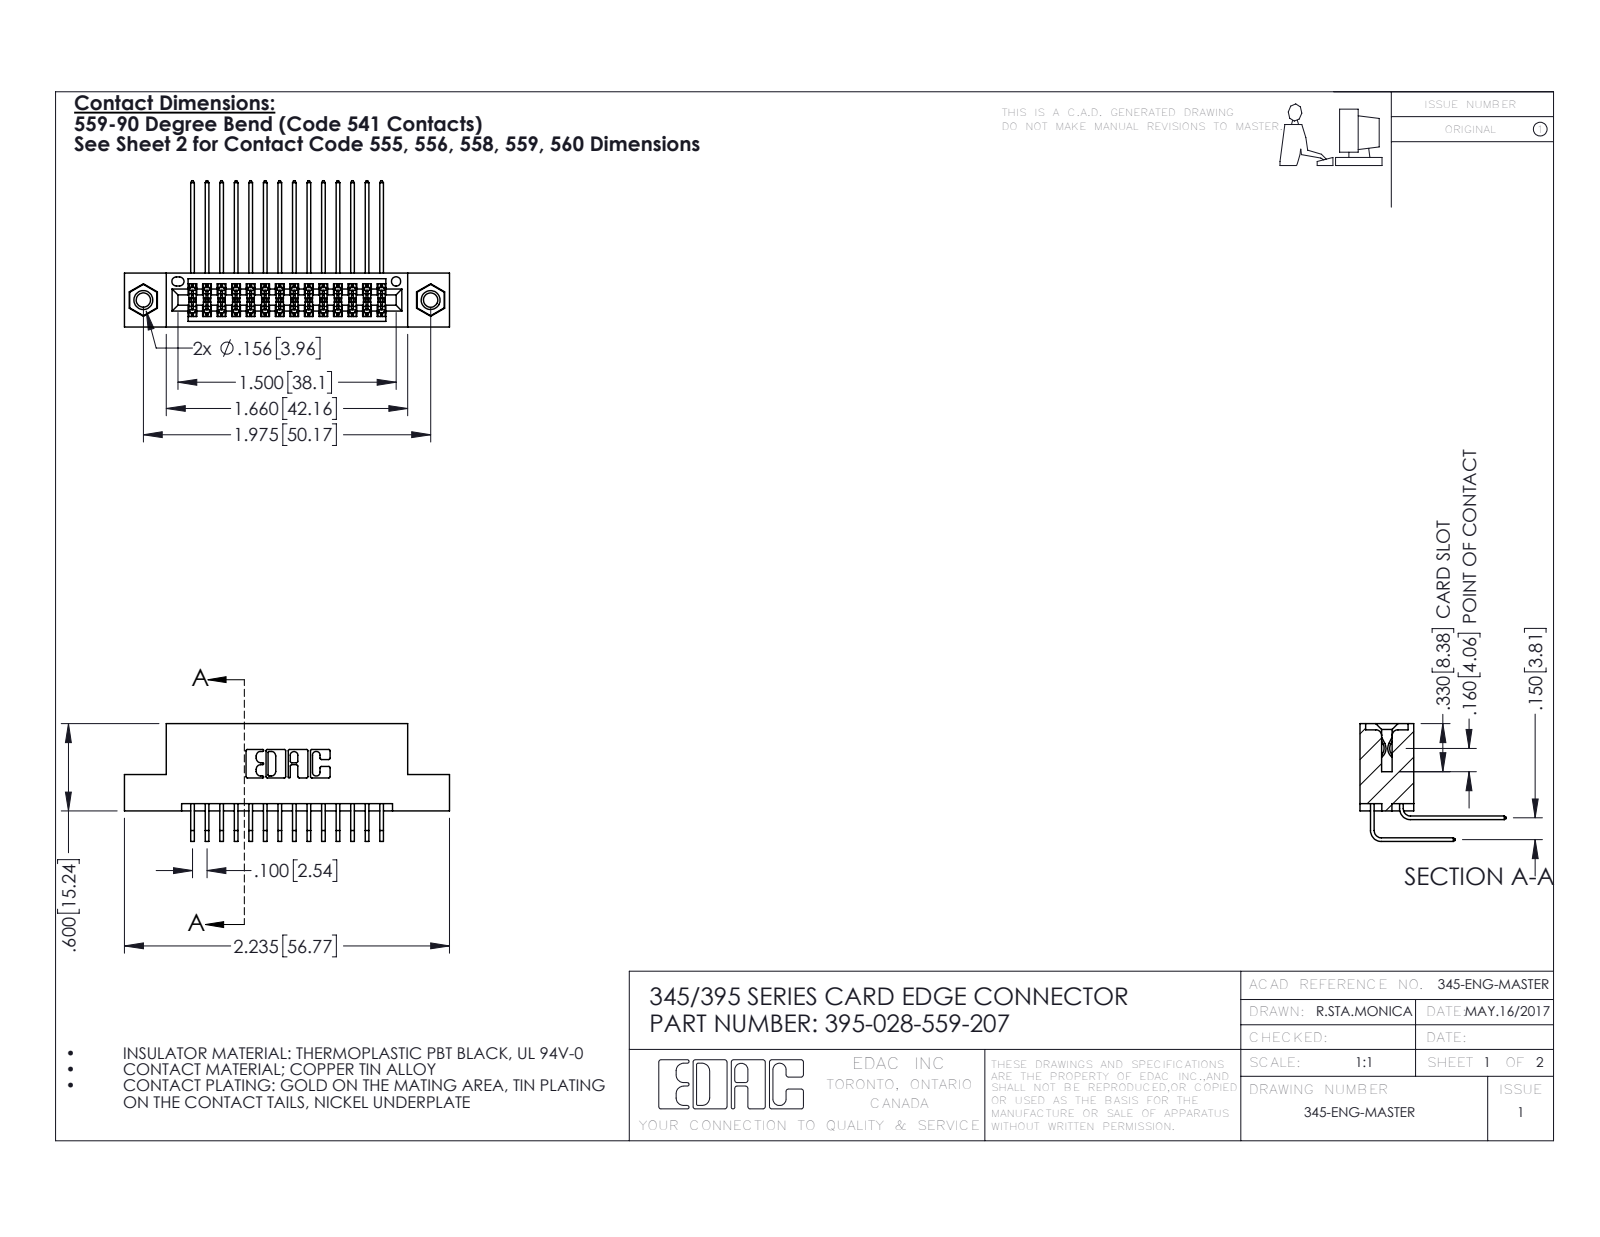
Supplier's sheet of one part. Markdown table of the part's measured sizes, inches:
| quantity | value |
| --- | --- |
| part name | 345-292-001_559 Tail - 2; 345-292-001_558 559 Tail - 1; 395-028-559-207; 345 Part_Flush Mounting Lugs - 0.156 Dia-TI (+1 more) |
| STEP written by | SolidWorks 2016 (CONFIG_CONTROL_DESIGN) |
| units | inches |
| bodies | 31 solids, 1642 faces (1092 planar, 534 cylindrical, 16 other) |
| overall size | 2.235 × 1.005 × 0.809 |
| volume | 0.33 in³ |
| surface area | 12.76 in² |
| round holes (diameter × count) | 0.098 × 2, 0.125 × 2, 0.156 × 2, 0.064 × 1 |
| round bosses / shafts (diameter × count) | 0.155 × 2 |
| partial cylindrical surfaces (radius × count) | 0.006 × 42, 0.01 × 22, 0.007 × 6, 0.031 × 6, 0.026 × 3, 0.014 × 2, 0.019 × 2, 0.022 × 2 |
| main face-to-face distances | 0.072, 0.298, 0.2, 0.37, 0.098, 0.272, 0.025, 0.225, 0.15, 0.175 |
| hole center spacings | 0.27, 1.742, 1.975 |
